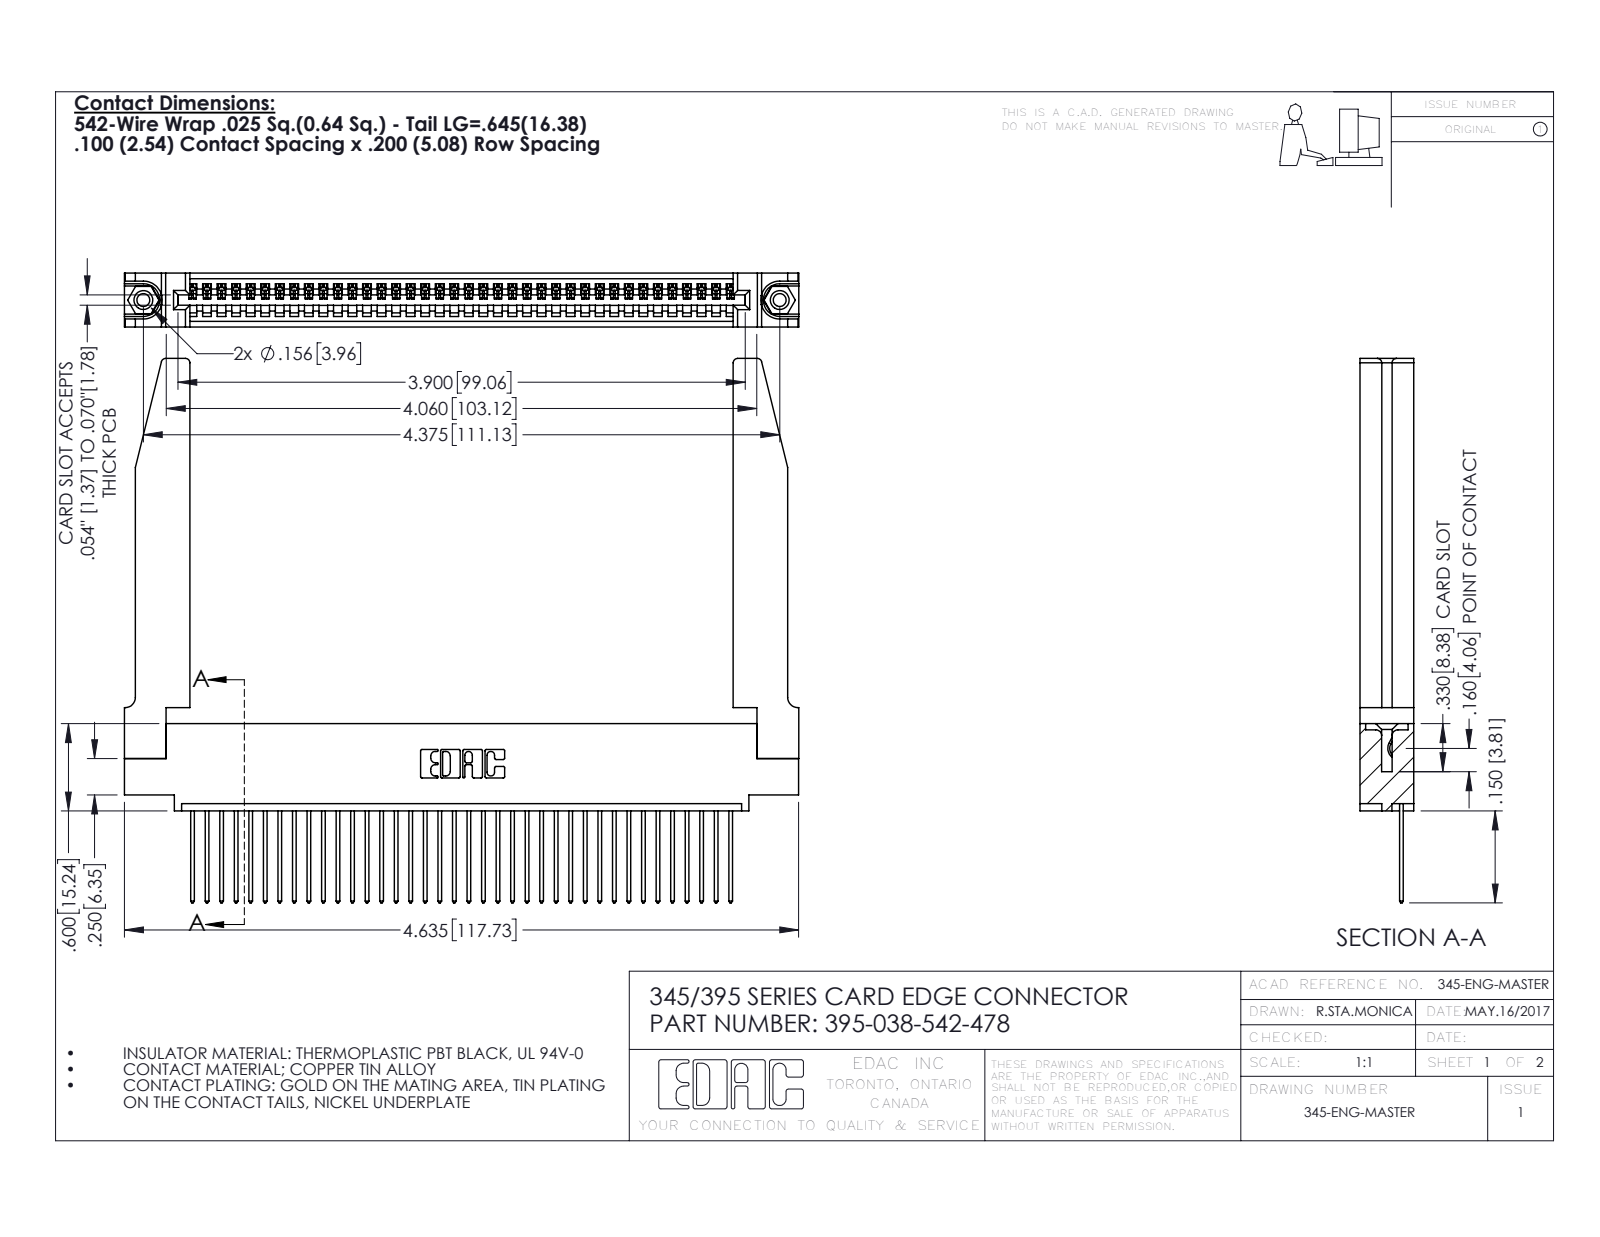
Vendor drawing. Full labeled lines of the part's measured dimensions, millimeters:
Part name (STEP PRODUCT): 395-038-542-478; 345-250-001_345-250-001-102; 345-292-001_345-293-142; 345-220-078_345-220-078 (+1 more)
STEP written by: SolidWorks 2016 (CONFIG_CONTROL_DESIGN)
Units: millimetres
Bodies: 43 solids, 2568 faces (1746 planar, 770 cylindrical, 52 other)
Overall size (bounding box): 117.8 × 95 × 9.4
Volume: 18 930 mm³ · Surface area: 22 250 mm²
Round holes (diameter × count): ⌀2.3 ×2, ⌀3.2 ×2, ⌀4 ×2, ⌀1.6 ×1
Round bosses / shafts (diameter × count): ⌀3.9 ×2
Partial cylindrical surfaces — rounded edges, fillets, slot ends (radius × count): R0.2 ×76, R0.3 ×76, R0.3 ×22, R0.8 ×8, R0.2 ×6, R0.8 ×6, R0.7 ×3, R0.8 ×2
Main face-to-face distances: 9.4, 1.8, 7.6, 2.5, 6.9, 0.6, 5.1, 5.7, 3.8, 3.8
Hole centre spacings: 6.9, 105.1, 111.1
